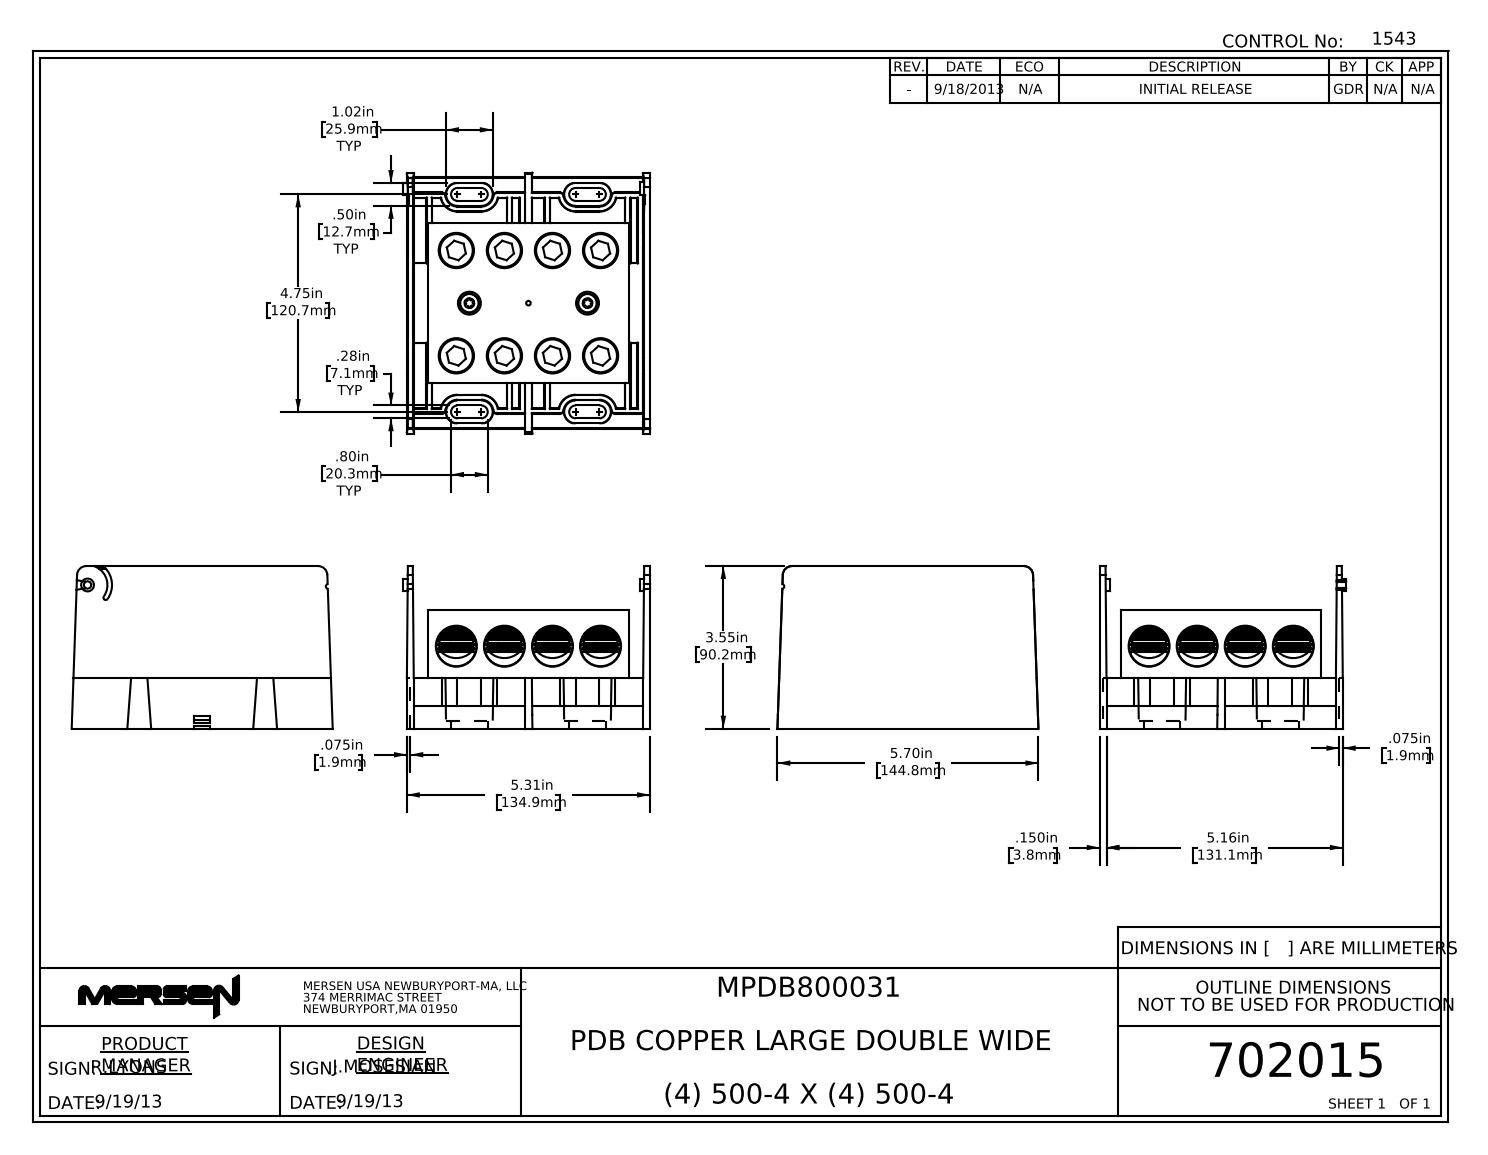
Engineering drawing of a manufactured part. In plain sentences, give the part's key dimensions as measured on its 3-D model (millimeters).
The part is named "702015rev". Its 3-D file was written by "SolidWorks 2017 (AUTOMOTIVE_DESIGN)". It is 14 solids with 1069 faces: 614 planar, 140 cylindrical and 315 other. Overall it measures 144.8 by 136.8 by 90.2 millimeters. Its volume is 535 500 cubic millimeters and its surface area 248 500 square millimeters. Round holes: 8 of diameter 19.1, 4 of diameter 4.9, 4 of diameter 22.2, 2 of diameter 6.9, 2 of diameter 12.7, 1 of diameter 4.1. Round bosses or shafts: 2 of diameter 10.8, 2 of diameter 7.1, 2 of diameter 5.7, 2 of diameter 4. Partial cylindrical surfaces (rounded edges, fillets, slot ends): 28 of radius 0.9, 20 of radius 0.3, 12 of radius 0.5, 12 of radius 0.8, 10 of radius 2.5, 8 of radius 3.6, 2 of radius 5.1, 2 of radius 11. The main face-to-face distances are 65.5, 131.1, 3.2, 10.2, 38.1, 13.3, 3.8, 62.2, 51.4, 11.8. The hole center spacings are 26.7, 53.3, 64.2, 30.1, 35.1, 54.6, 58.4, 78.4.
